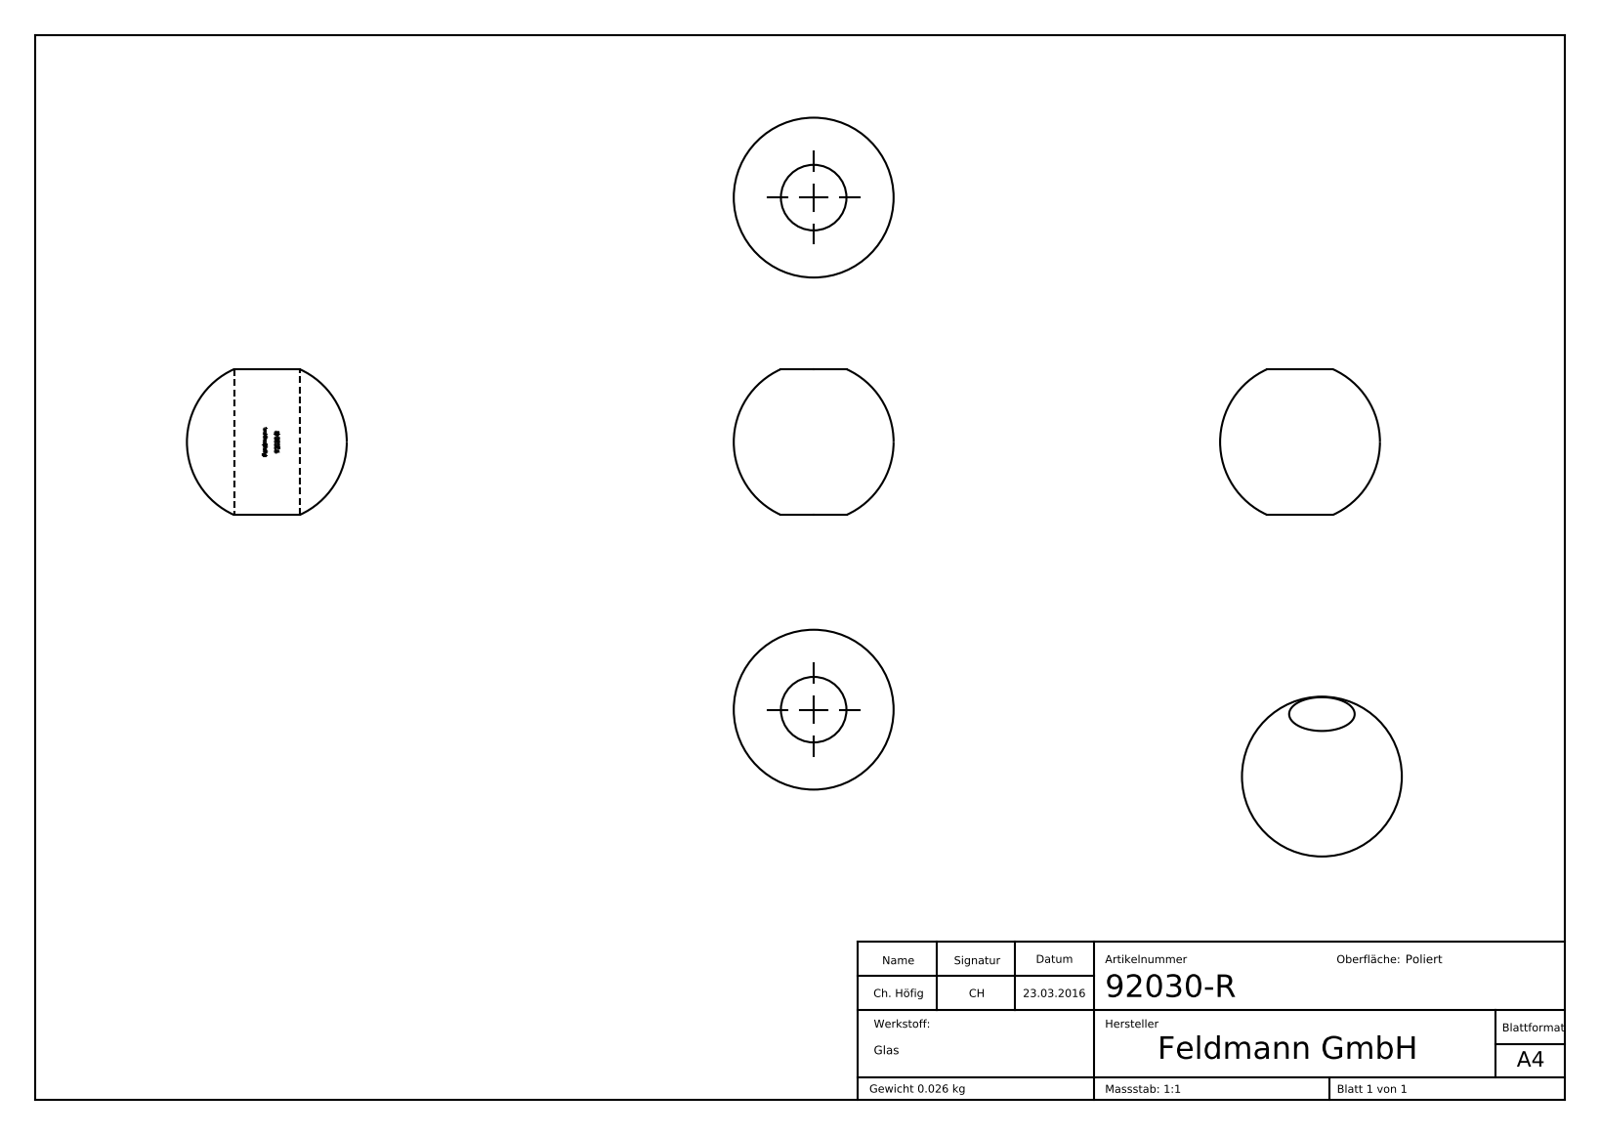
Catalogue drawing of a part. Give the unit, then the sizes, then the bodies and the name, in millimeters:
Units: millimetres
Overall size (bounding box): 30 × 30 × 27.36
Round holes (diameter × count): ⌀12.3 ×1
Partial cylindrical surfaces — rounded edges, fillets, slot ends (radius × count): R6.25 ×1
Main face-to-face distances: 1.78, 2.84, 0.83, 0.44, 0.99, 0.67, 1.21, 4.05, 2.77, 2.45
Volume: 10 727 mm³ · Surface area: 3 642 mm²
Bodies: 1 solid, 207 faces (81 planar, 24 cylindrical, 102 other)
Part name (STEP PRODUCT): 92030-R
STEP written by: SolidWorks 2015 (CONFIG_CONTROL_DESIGN)
